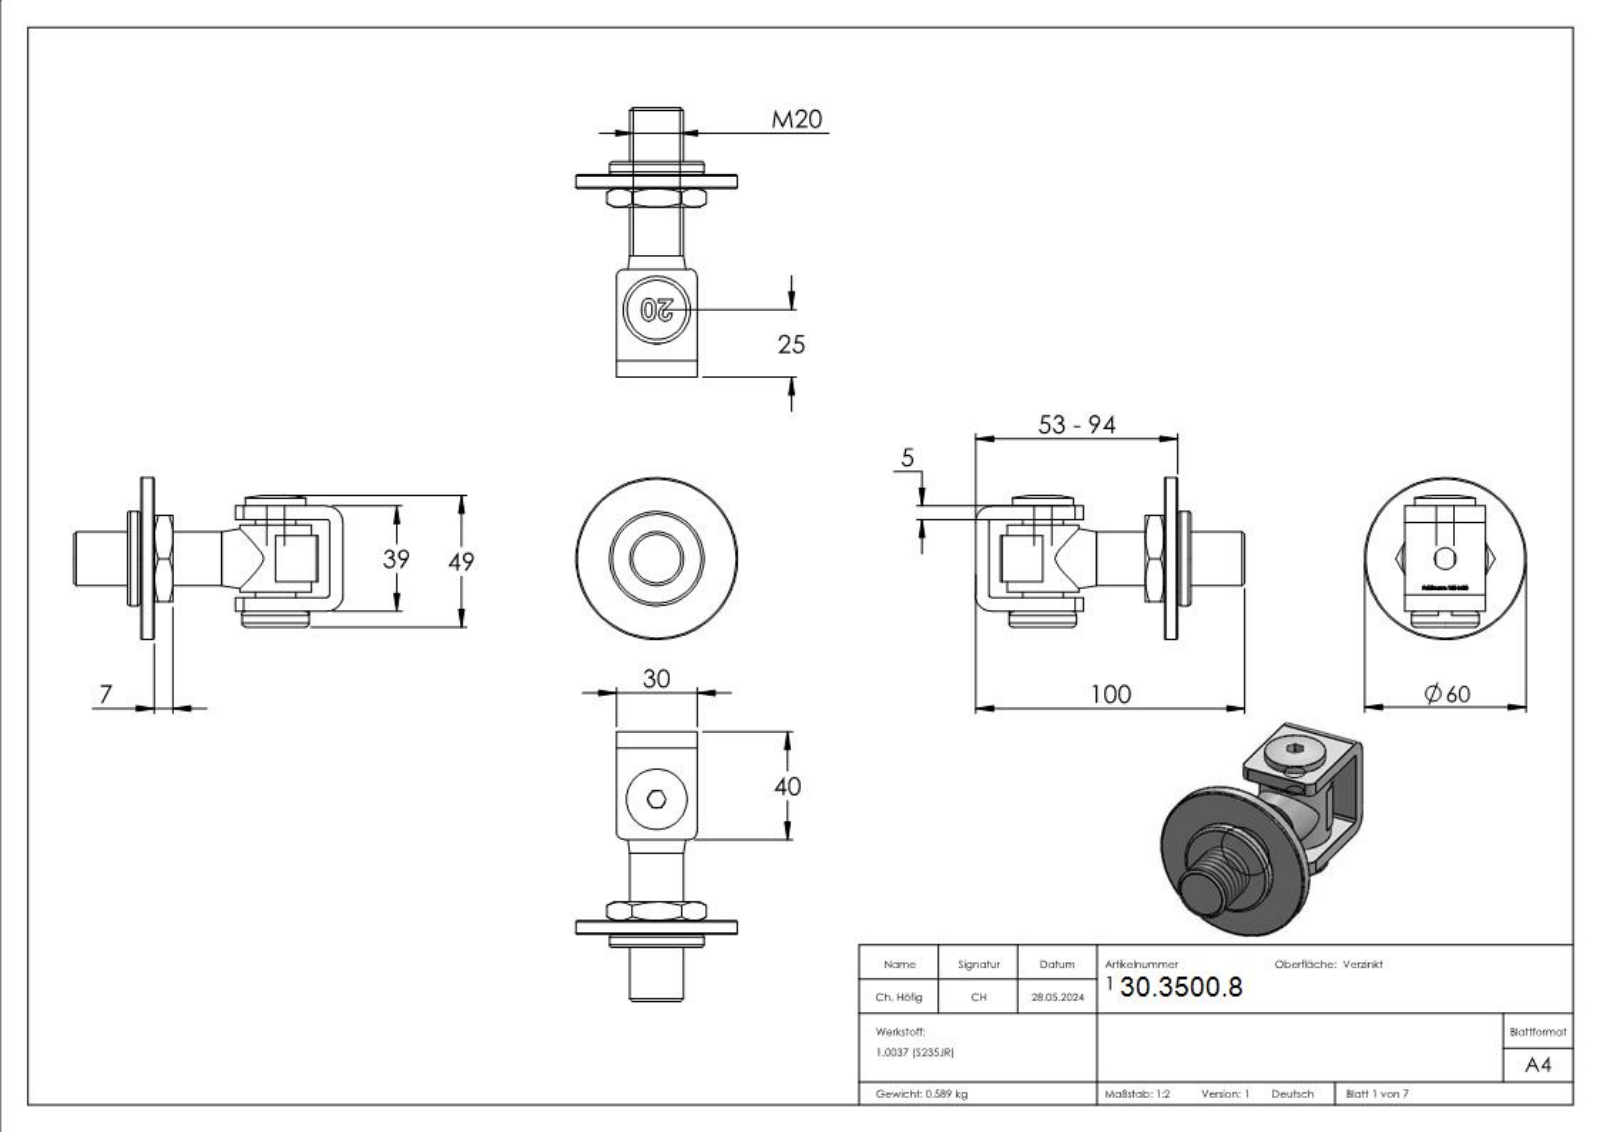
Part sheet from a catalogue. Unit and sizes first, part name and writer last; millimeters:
Units: millimetres
Overall size (bounding box): 100 × 60 × 60
Round holes (diameter × count): ⌀6.8 ×1, ⌀8 ×1, ⌀9 ×1, ⌀14.9 ×1, ⌀15 ×1, ⌀17.5 ×1, ⌀26.5 ×1, ⌀29.4 ×1
Round bosses / shafts (diameter × count): ⌀25 ×2, ⌀60 ×1, ⌀35 ×1, ⌀27.4 ×1, ⌀22.5 ×1, ⌀20 ×1, ⌀8 ×1
Partial cylindrical surfaces — rounded edges, fillets, slot ends (radius × count): R1 ×2, R3 ×2, R6 ×2, R15 ×2, R3.1 ×1, R10 ×1
Main face-to-face distances: 5, 34, 70.1, 40, 32, 7, 30, 39, 45, 30.1
Volume: 75 545 mm³ · Surface area: 32 099 mm²
Bodies: 7 solids, 327 faces (173 planar, 32 cylindrical, 122 other)
Part name (STEP PRODUCT): 155-MXX Teil5_155-M20 Teil5; 155-MXX Teil3_155-M20 Teil3; 155-M20; 155-MXX Teil2_155-M20 Teil2 (+2 more)
STEP written by: SolidWorks 2018 (CONFIG_CONTROL_DESIGN)
